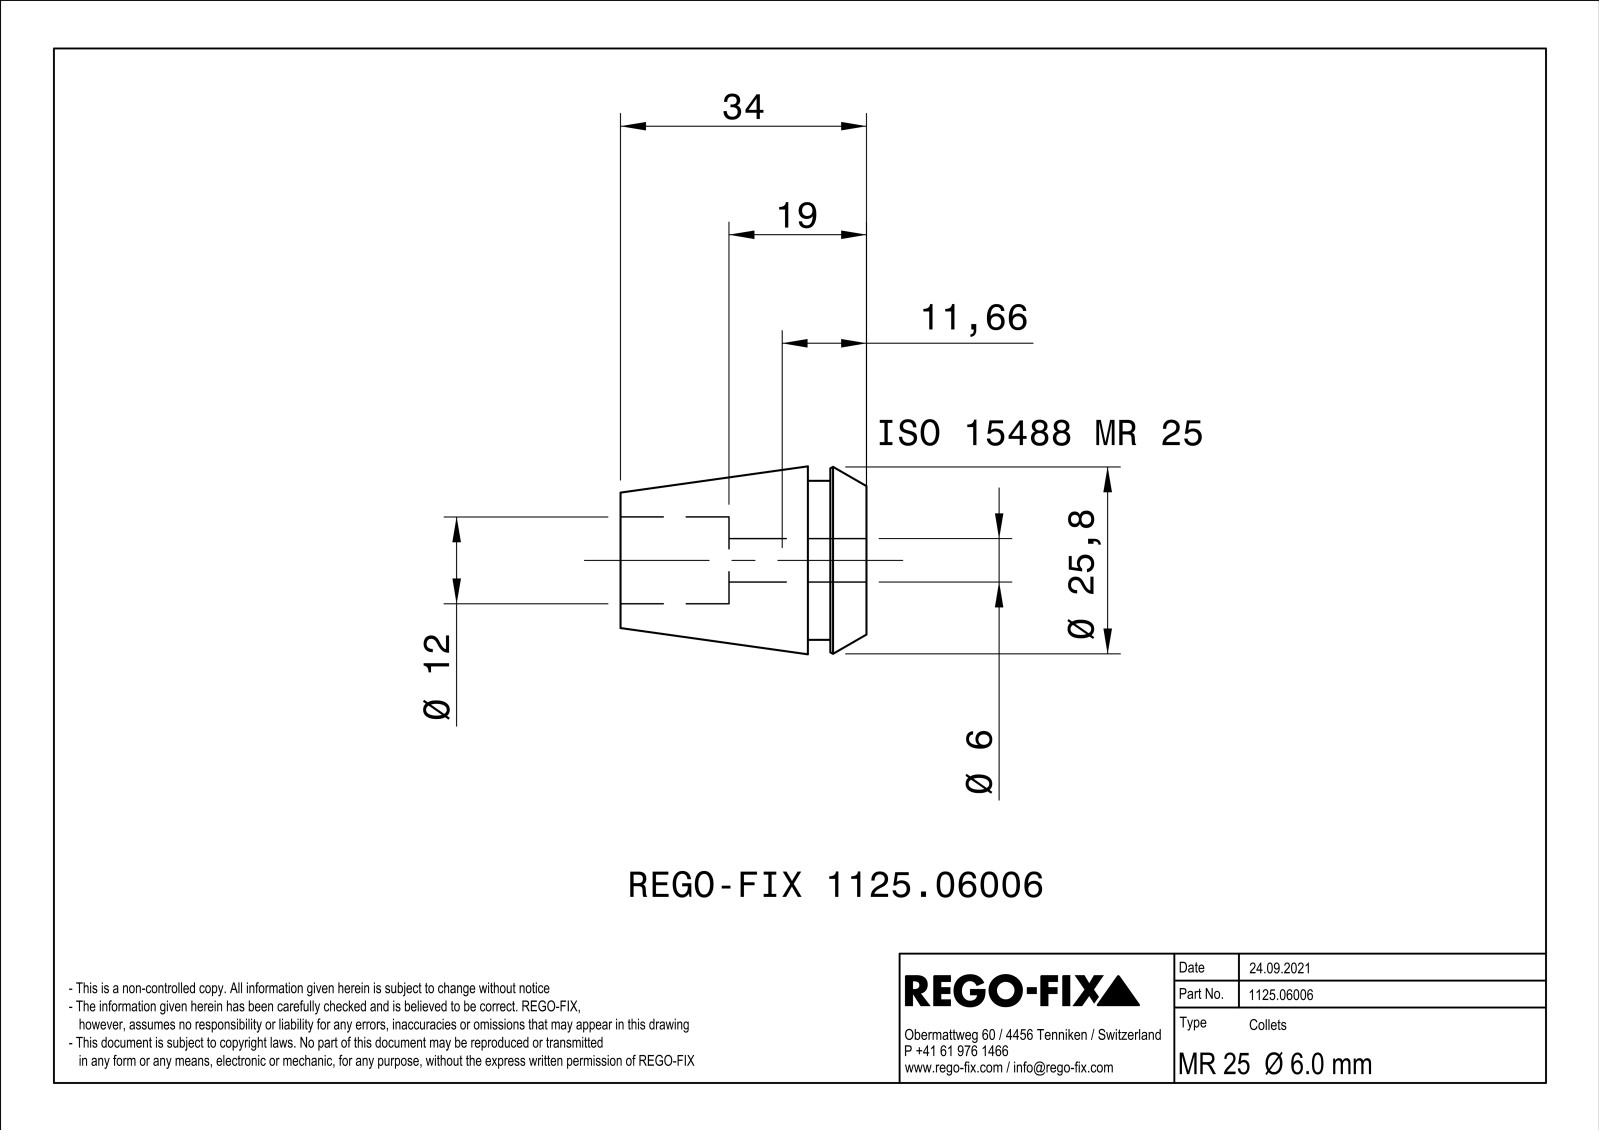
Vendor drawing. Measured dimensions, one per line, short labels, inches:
name: NOCUT
written by: SIEMENS PLM Software Solid Edge ST10 (AUTOMOTIVE_DESIGN)
unit: in
bodies: 1 solid, 256 faces (88 planar, 48 cylindrical, 120 other)
size: 1.339 × 1.023 × 1.023
volume: 0.56 in³; area: 13.87 in²
holes: 1× ⌀0.472
bosses: 1× ⌀0.866
rounds: 12× R0.016, 1× R0.118
face distances: 0.031, 0.032, 0.031, 0.319, 1.339, 1.02, 0.197, 0.122, 1.142, 0.748
